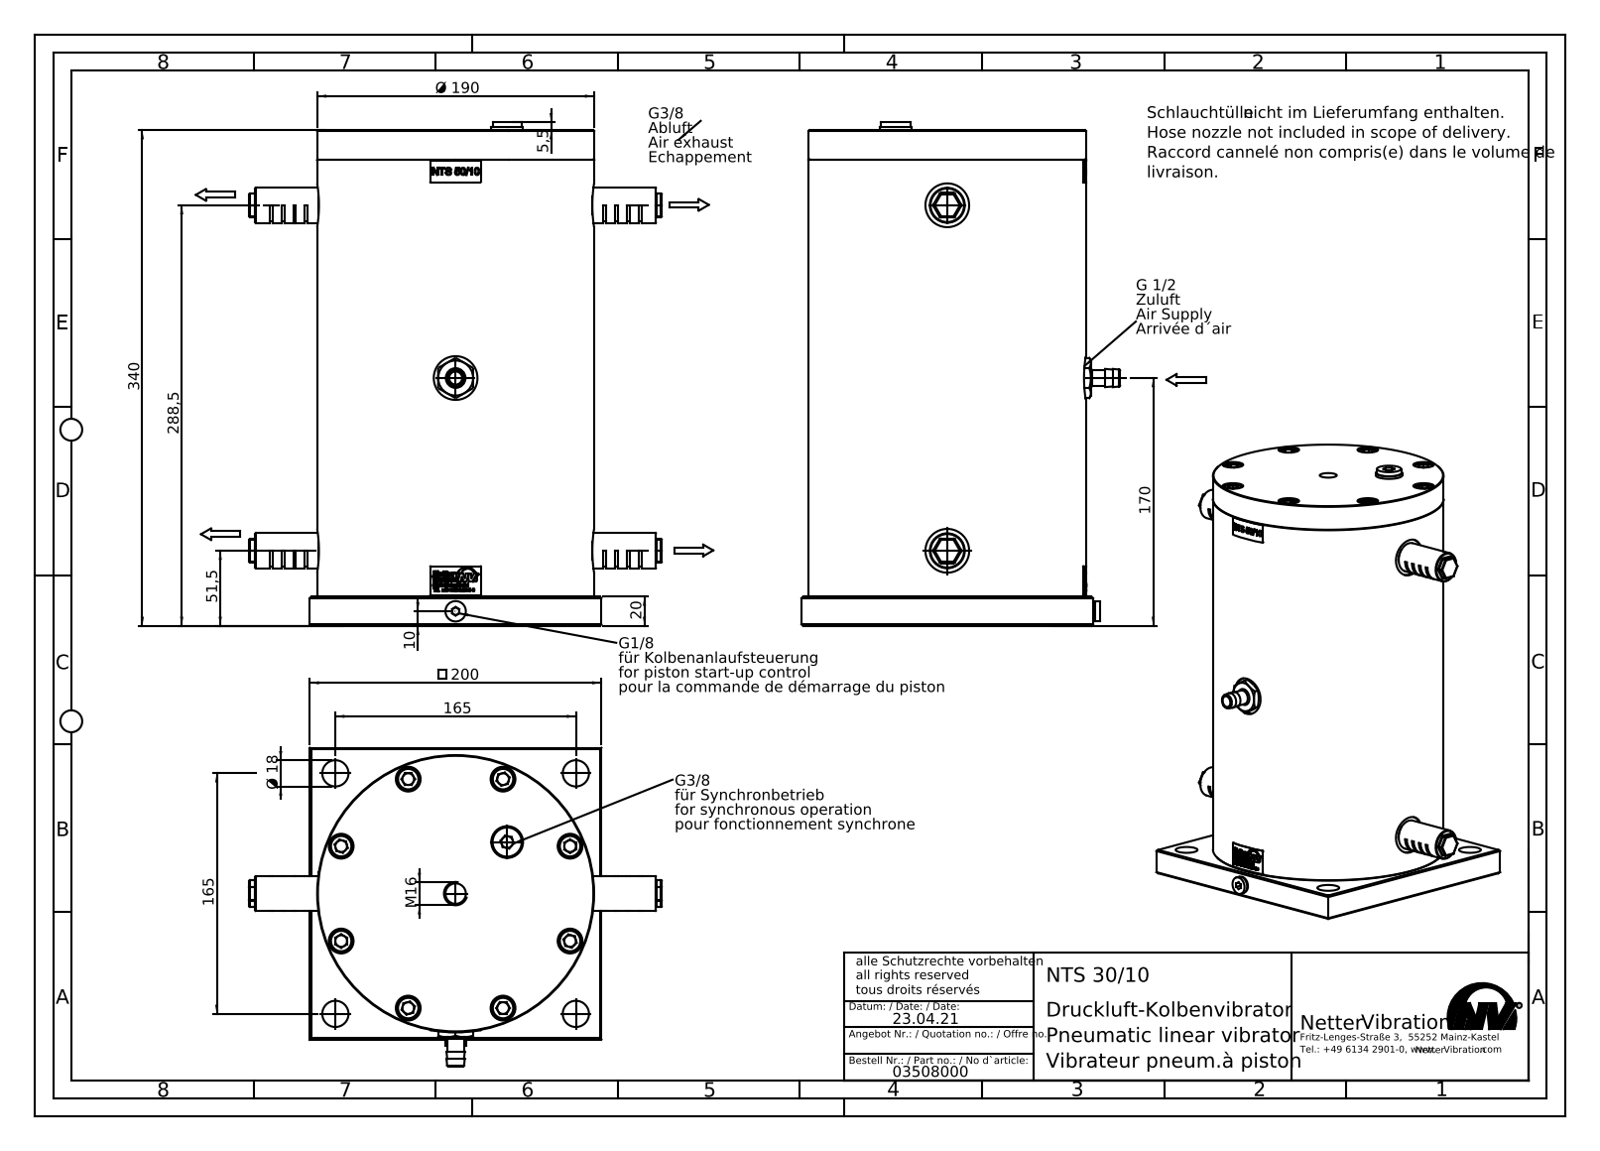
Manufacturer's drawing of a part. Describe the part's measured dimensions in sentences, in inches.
The part is named "NTS 30-10 Kolbenvibrator #03508000". Its 3-D file was written by "SolidWorks 2015 (AUTOMOTIVE_DESIGN)". It is 30 solids with 1267 faces: 434 planar, 479 cylindrical and 354 other. Overall it measures 13.602 by 11.142 by 8.602 inches. Its volume is 602.7 cubic inches and its surface area 774.9 square inches. Round holes: 8 of diameter 0.335, 8 of diameter 0.413, 8 of diameter 0.433, 8 of diameter 0.669, 4 of diameter 0.709, 3 of diameter 0.589, 3 of diameter 1.181, 2 of diameter 0.472, 1 of diameter 0.197, 1 of diameter 0.236, 1 of diameter 0.337, 1 of diameter 0.354. Round bosses or shafts: 8 of diameter 0.63, 8 of diameter 0.394, 2 of diameter 0.945, 2 of diameter 0.656, 1 of diameter 7.48, 1 of diameter 0.858, 1 of diameter 0.825, 1 of diameter 0.787. Partial cylindrical surfaces (rounded edges, fillets, slot ends): 68 of radius 0.02, 2 of radius 0.433, 1 of radius 3.748. The main face-to-face distances are 11.811, 0.787, 12.598, 0.748, 0.039, 13.346, 12.559, 13.386, 7.874, 0.433. The hole center spacings are 1.974, 3.346, 4.531, 4.733, 6.183, 6.638, 7.791, 2.561.
